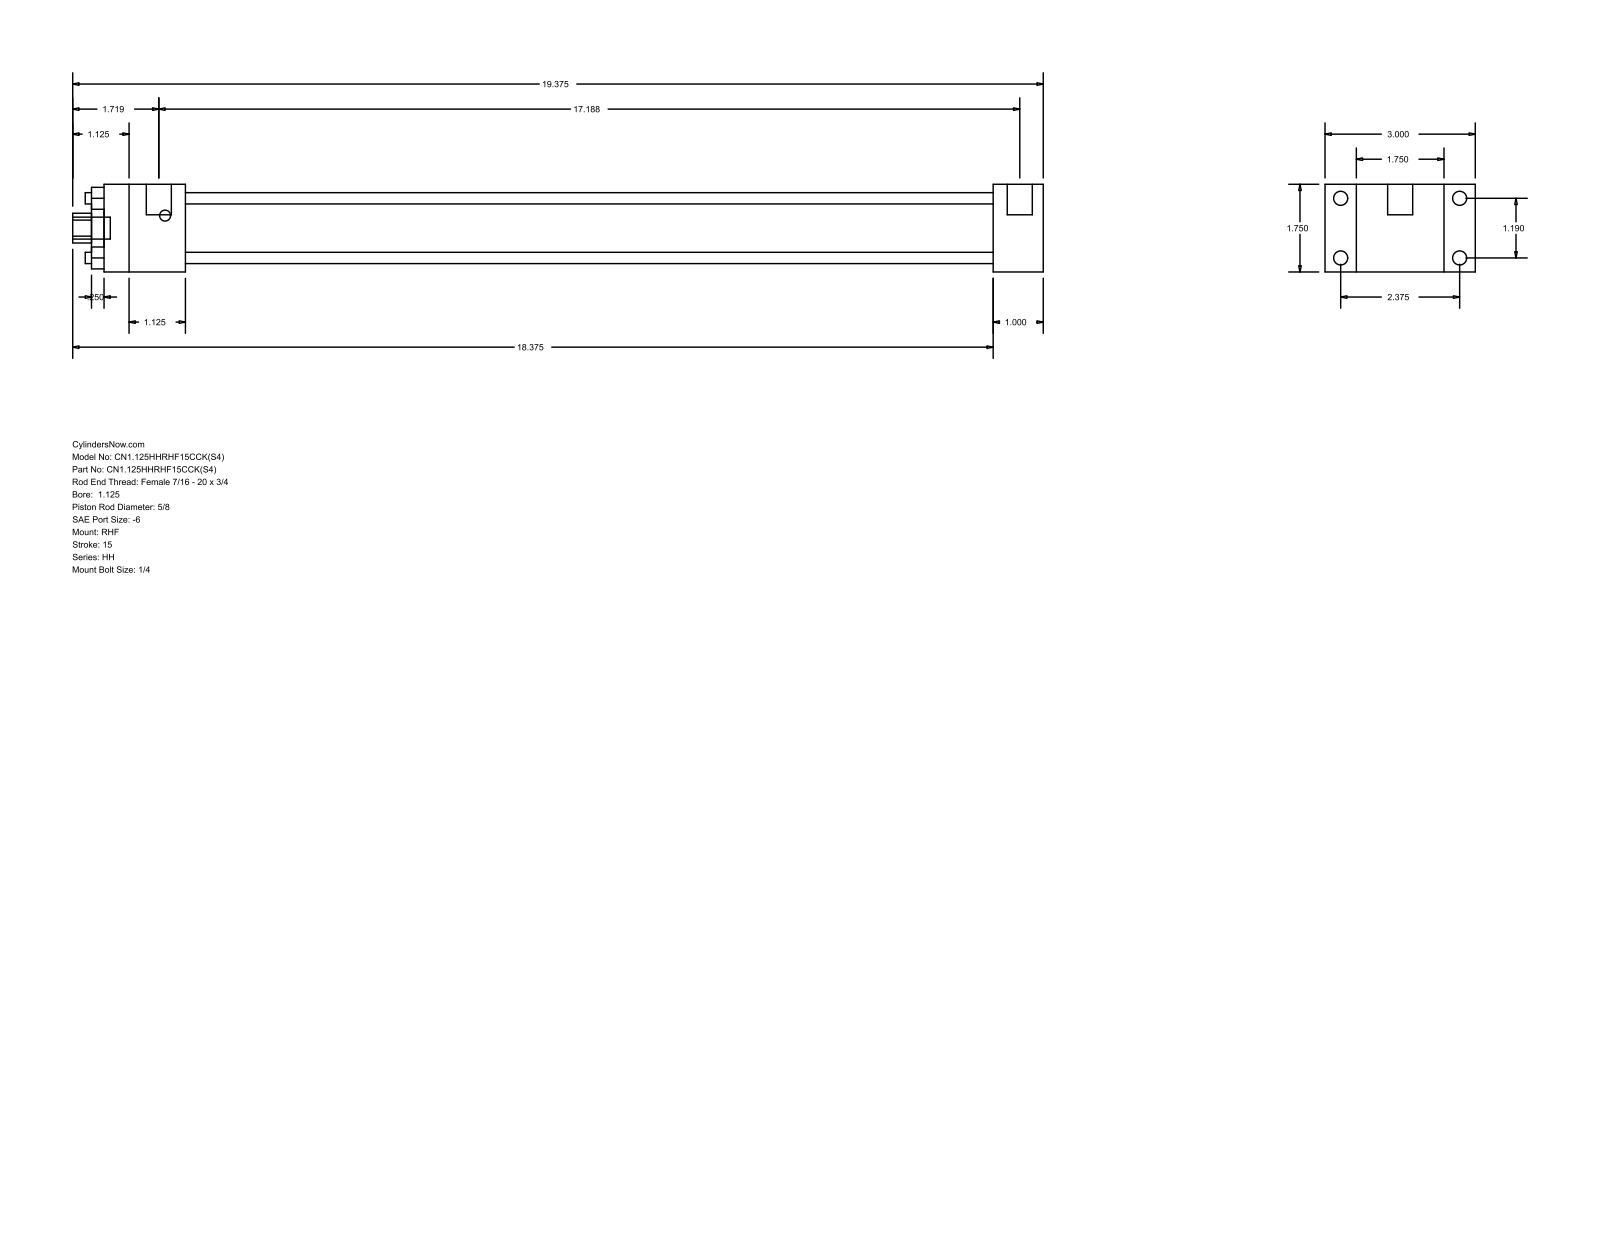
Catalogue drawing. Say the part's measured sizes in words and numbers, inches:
The part is named "HH_RHF__0112_0.625". Its 3-D file was written by "GSSL Pune (CONFIG_CONTROL_DESIGN)". It is 0 solids with 88 faces: 60 planar, 28 cylindrical and 0 other. Overall it measures 19.375 by 3 by 1.75 inches. Round holes: 4 of diameter 0.225, 1 of diameter 0.625, 1 of diameter 1.125, 1 of diameter 1.375. Round bosses or shafts: 4 of diameter 0.281, 4 of diameter 0.219, 2 of diameter 0.5, 1 of diameter 0.437. Partial cylindrical surfaces (rounded edges, fillets, slot ends): 1 of radius 0.297. The main face-to-face distances are 1.75, 0.625, 2.375, 1, 3, 16.125, 17.125, 1.625, 17.75, 18.75. The hole center spacings are 0.841, 1.19, 1.683.
